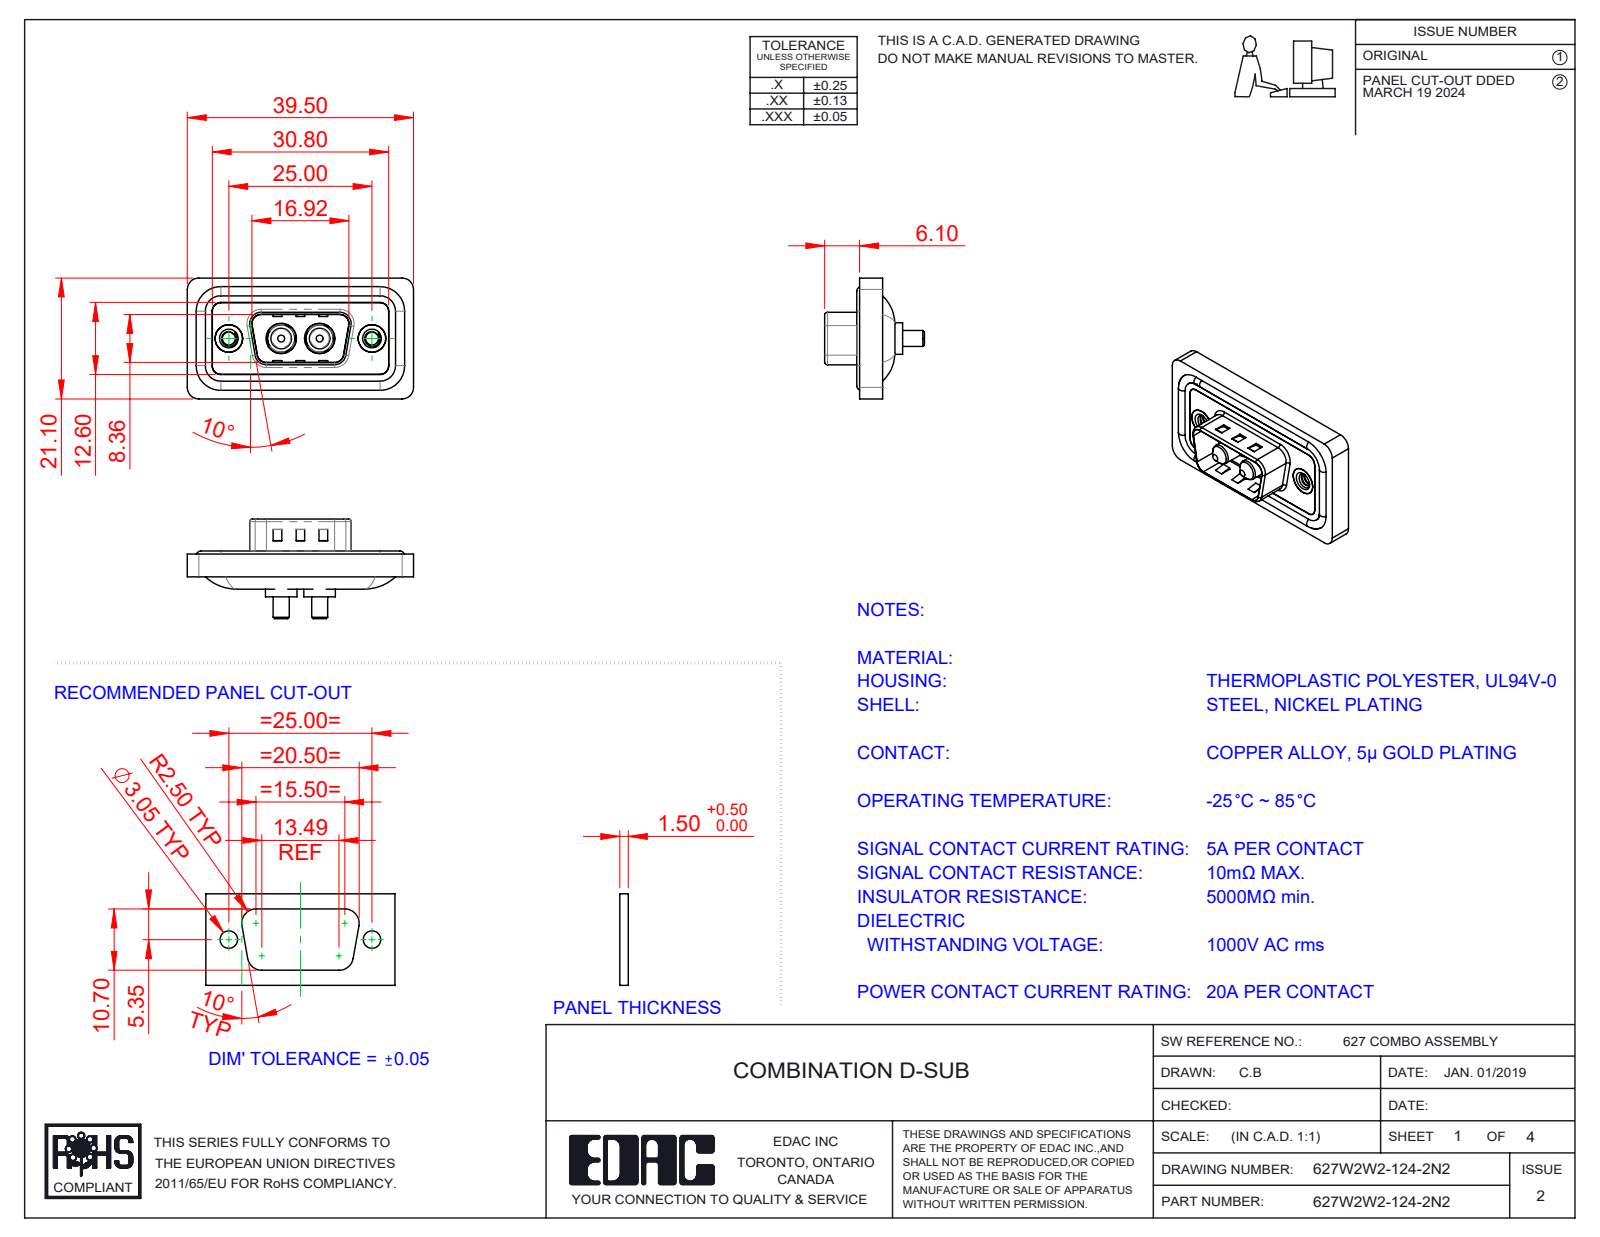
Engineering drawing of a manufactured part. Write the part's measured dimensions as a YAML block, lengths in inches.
part_name: "627Combo Shell Front_09 Contacts; 627Combo Housing_2W2; 627W2W2-124-2N2; 627Combo Threaded Rivet_2 (+3 more)"
step_written_by: "SolidWorks 2023 (CONFIG_CONTROL_DESIGN)"
units: inches
bodies: {solids: 11, faces: 489, planar: 165, cylindrical: 218, other: 106}
overall_size: [1.555, 0.831, 0.685]
volume: 0.272
surface_area: 10.83
round_holes:
  - {diameter: 0.089, count: 2}
  - {diameter: 0.157, count: 2}
  - {diameter: 0.189, count: 2}
  - {diameter: 0.191, count: 2}
  - {diameter: 0.197, count: 2}
  - {diameter: 0.209, count: 2}
round_bosses_or_shafts:
  - {diameter: 0.063, count: 4}
  - {diameter: 0.217, count: 2}
  - {diameter: 0.205, count: 2}
  - {diameter: 0.193, count: 2}
  - {diameter: 0.187, count: 2}
  - {diameter: 0.148, count: 2}
  - {diameter: 0.142, count: 2}
  - {diameter: 0.11, count: 2}
partial_cylinders:
  - {radius: 0.059, count: 22}
  - {radius: 0.079, count: 18}
  - {radius: 0.02, count: 8}
  - {radius: 0.063, count: 8}
  - {radius: 0.01, count: 4}
  - {radius: 0.024, count: 4}
  - {radius: 0.026, count: 4}
  - {radius: 0.035, count: 4}
face_to_face_distances: [0.016, 0.043, 0.114, 0.122, 0.02, 0.063, 0.059, 0.157, 0.098, 0.028]
hole_center_spacings: [0.36, 0.624, 0.265, 0.984]
